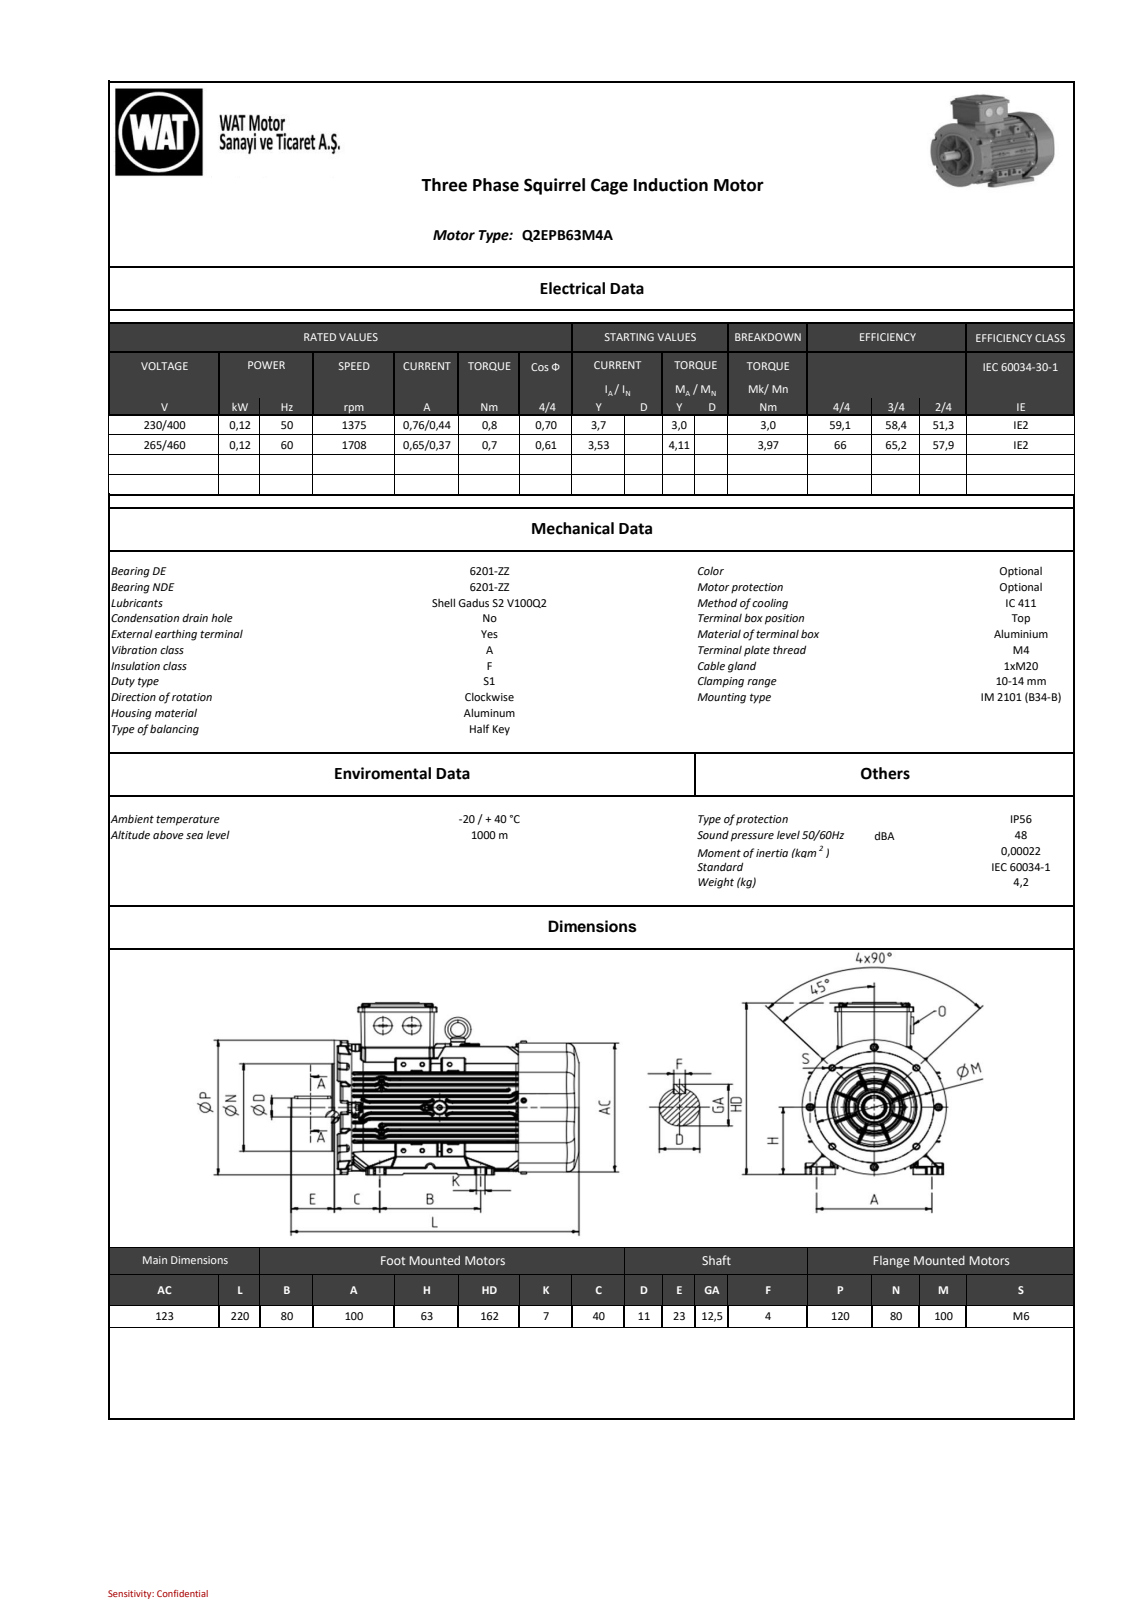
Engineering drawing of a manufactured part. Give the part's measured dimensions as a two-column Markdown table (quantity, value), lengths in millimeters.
| quantity | value |
| --- | --- |
| part name | QS63PBGMM |
| STEP written by | UNIX (AUTOMOTIVE_DESIGN) |
| units | millimeters |
| bodies | 11 solids, 3042 faces (0 planar, 0 cylindrical, 3042 other) |
| overall size | 219.45 × 161.1 × 128 |
| volume | 71 618 mm³ |
| surface area | 406 197 mm² |
